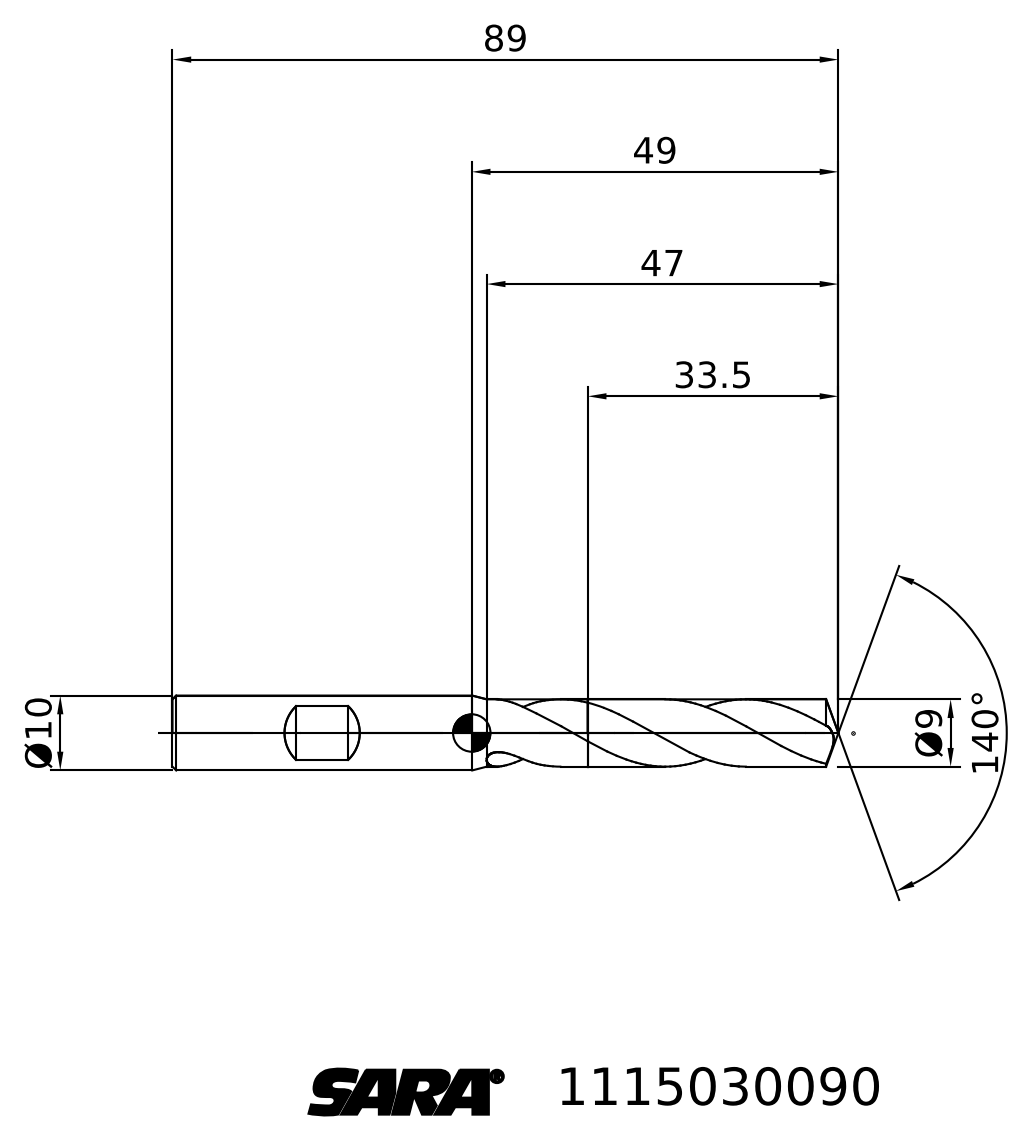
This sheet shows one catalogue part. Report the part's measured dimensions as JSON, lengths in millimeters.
{"step_written_by": "TDM (AUTOMOTIVE_DESIGN)", "units": "millimeters", "bodies": {"solids": 2, "faces": 30, "planar": 6, "cylindrical": 0, "other": 24}, "overall_size": [89, 22.77, 14.19], "volume_mm3": 5200, "surface_area_mm2": 2919, "face_to_face_distances": [55.5]}
